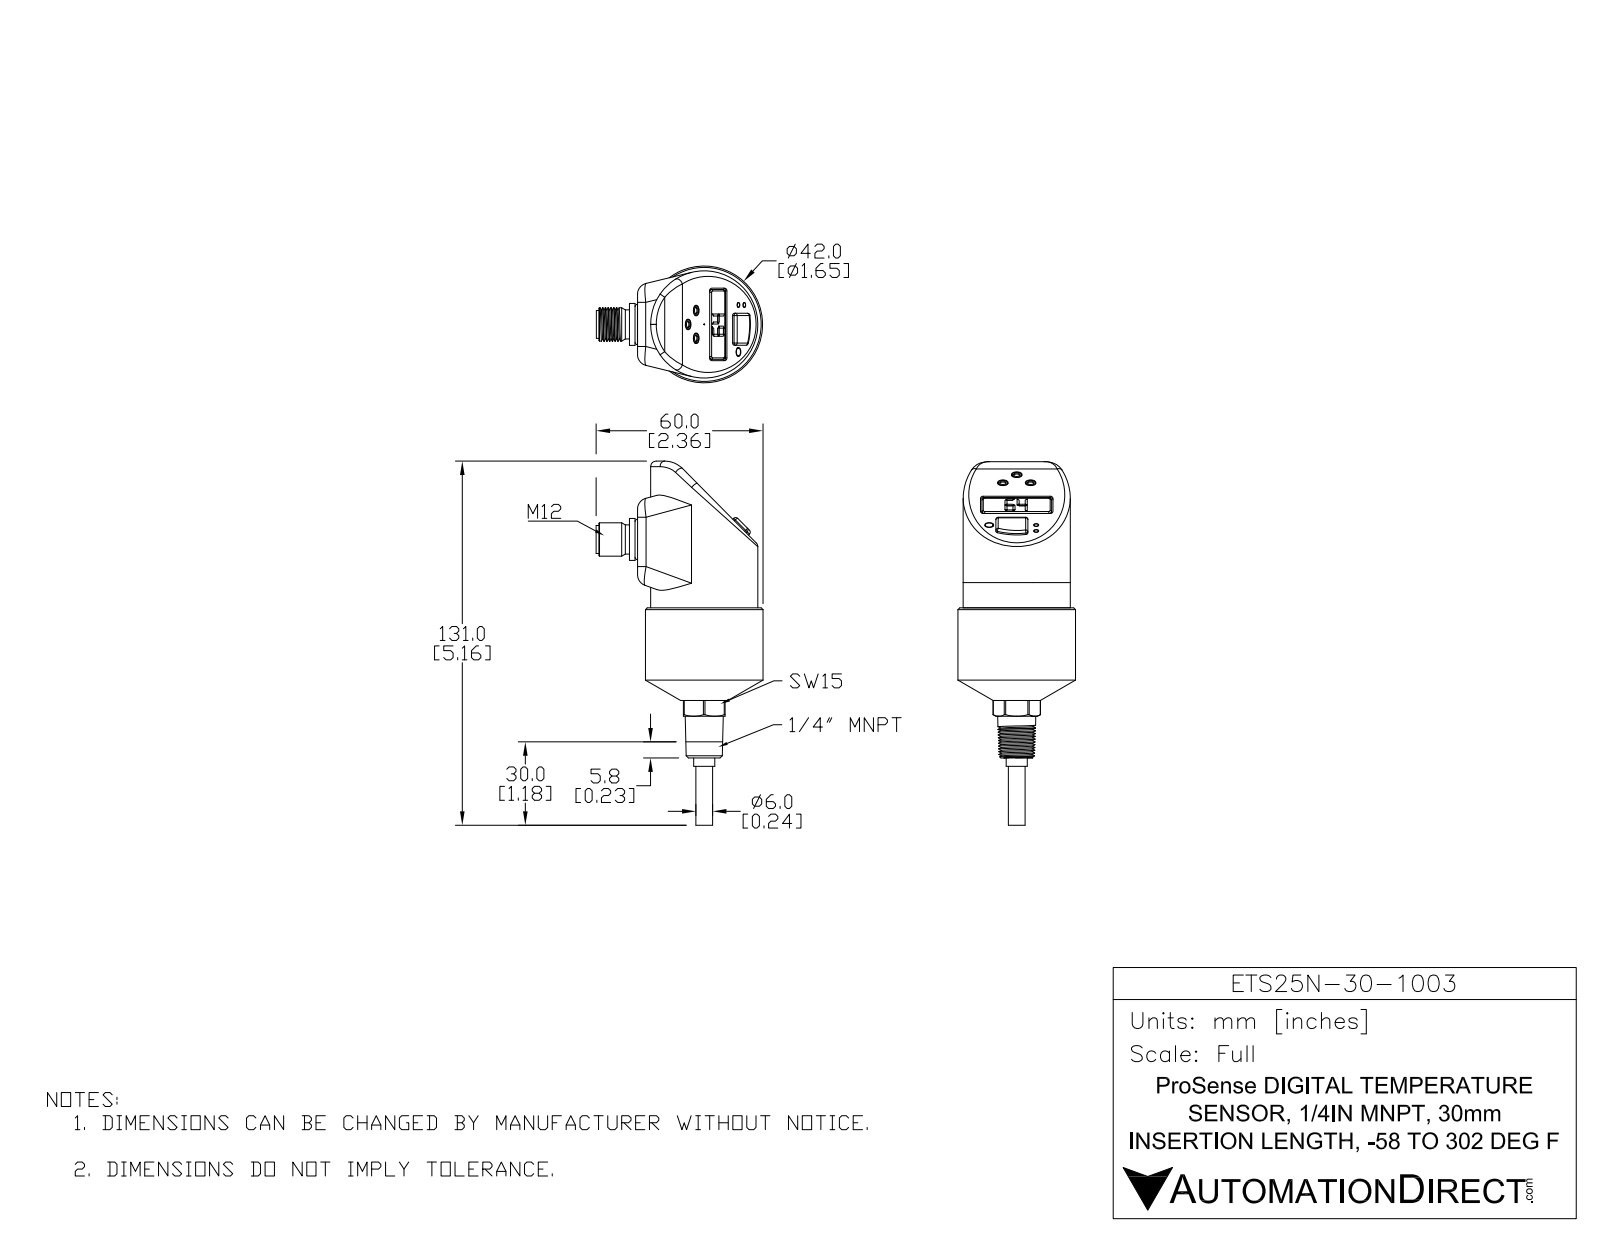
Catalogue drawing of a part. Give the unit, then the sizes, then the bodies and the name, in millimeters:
Units: millimetres
Overall size (bounding box): 130.8 × 59.95 × 42.3
Round holes (diameter × count): ⌀8.45 ×1
Round bosses / shafts (diameter × count): ⌀1.4 ×4, ⌀1 ×4, ⌀42.3 ×1, ⌀38.55 ×1, ⌀15.1 ×1, ⌀14.56 ×1, ⌀12 ×1, ⌀11 ×1
Partial cylindrical surfaces — rounded edges, fillets, slot ends (radius × count): R1 ×8, R0.8 ×7, R0.5 ×4, R3.99 ×4, R7 ×4, R0.61 ×1, R2 ×1, R8.5 ×1
Main face-to-face distances: 15, 0.9, 2, 2.9, 1.5, 54, 13.9, 4, 1.1, 3.1
Volume: 101 659 mm³ · Surface area: 18 058 mm²
Bodies: 2 solids, 323 faces (138 planar, 95 cylindrical, 90 other)
Part name (STEP PRODUCT): ETS25N-30-1003
STEP written by: SolidWorks 2016 (AUTOMOTIVE_DESIGN)
